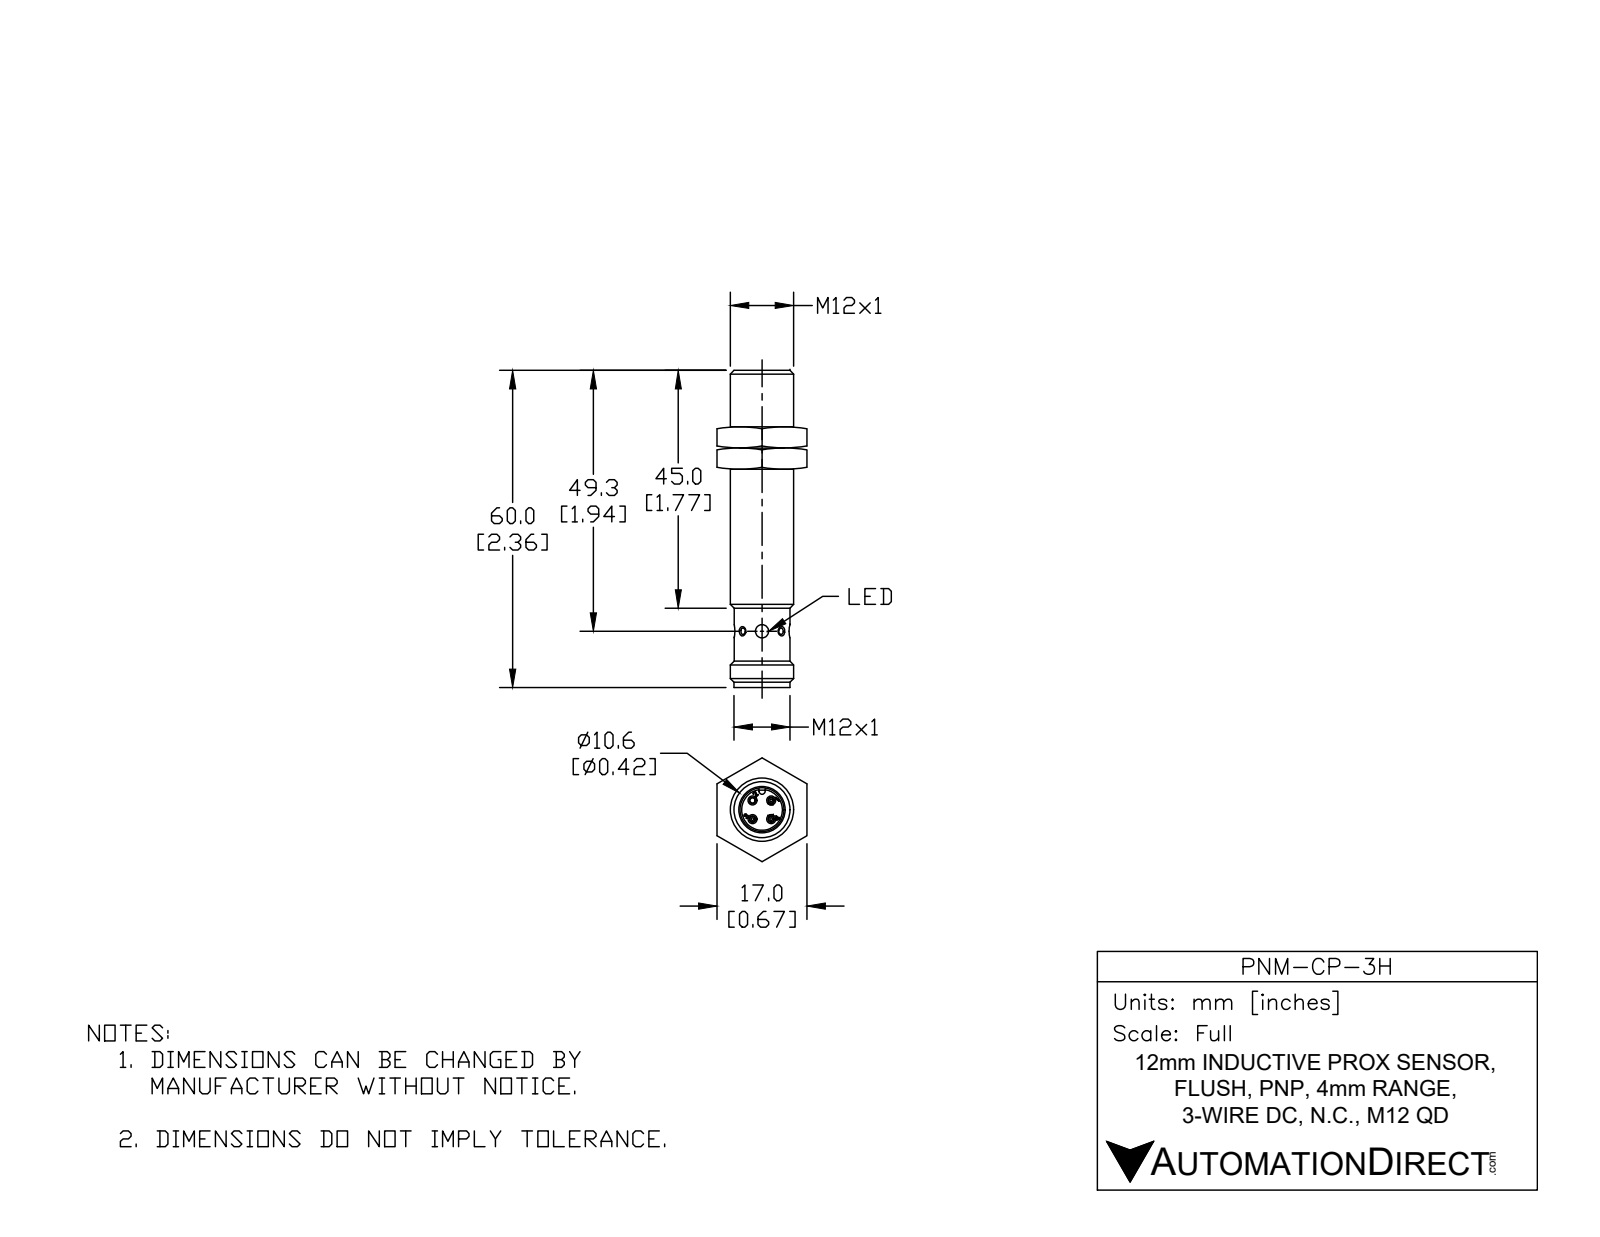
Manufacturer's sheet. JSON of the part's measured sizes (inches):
{"part_name": "PNM-CP-3H", "step_written_by": "SolidWorks 2017 (AUTOMOTIVE_DESIGN)", "units": "inches", "bodies": {"solids": 1, "faces": 479, "planar": 119, "cylindrical": 134, "other": 226}, "overall_size": [2.362, 0.472, 0.472], "volume_in3": 0.35, "surface_area_in2": 10.25, "round_holes": [[0.043, 3], [0.04, 2], [0.098, 2], [0.038, 1], [0.04, 1], [0.327, 1], [0.394, 1], [0.401, 1]], "round_bosses_or_shafts": [[0.039, 9], [0.472, 1], [0.417, 1], [0.415, 1], [0.4, 1], [0.392, 1], [0.39, 1], [0.376, 1]], "partial_cylinders_radius": [[0.004, 36], [0.024, 1], [0.031, 1], [0.161, 1]], "face_to_face_distances": [0.039, 1.87, 1.831, 0.018, 0.022, 1.852, 2.323, 0.142, 2.012, 1.994], "hole_center_spacings": [0.098, 0.139, 0.197]}
